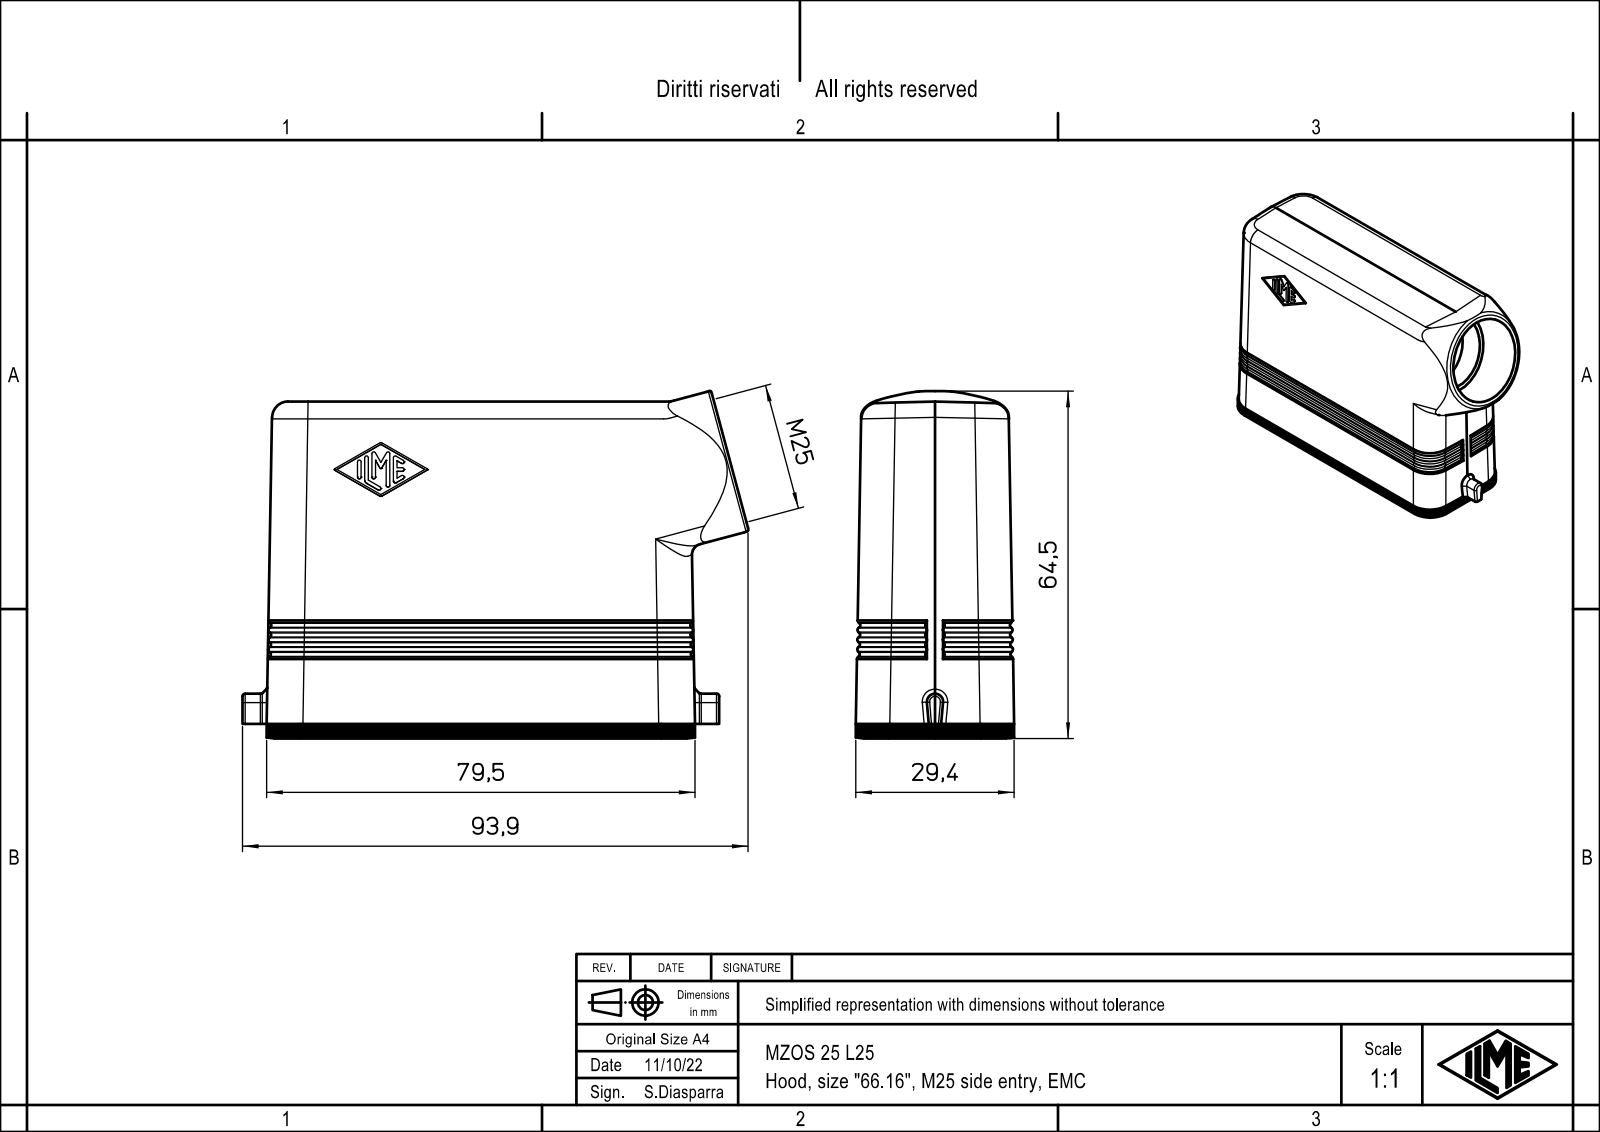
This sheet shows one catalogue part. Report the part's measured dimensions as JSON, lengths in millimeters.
{"part_name": "CZ_MZ Tüllengehäuse 1 Bügel", "step_written_by": "Autodesk Inventor 7 (AUTOMOTIVE_DESIGN)", "units": "millimeters", "bodies": {"solids": 1, "faces": 330, "planar": 155, "cylindrical": 88, "other": 87}, "overall_size": [98.01, 55.88, 29.41], "volume_mm3": 43845, "surface_area_mm2": 28044, "round_holes": [[2.46, 4], [3.5, 4], [23, 1], [25, 1]], "round_bosses_or_shafts": [[3.6, 1]], "partial_cylinders_radius": [[0.25, 14], [2, 8], [4, 8], [1.25, 4], [3.3, 2], [4.2, 2]], "face_to_face_distances": [3, 26.4, 29.4, 23.4, 1.13, 6.75, 9.75, 76.5, 66.75, 69.75], "hole_center_spacings": [16, 66, 67.91]}
